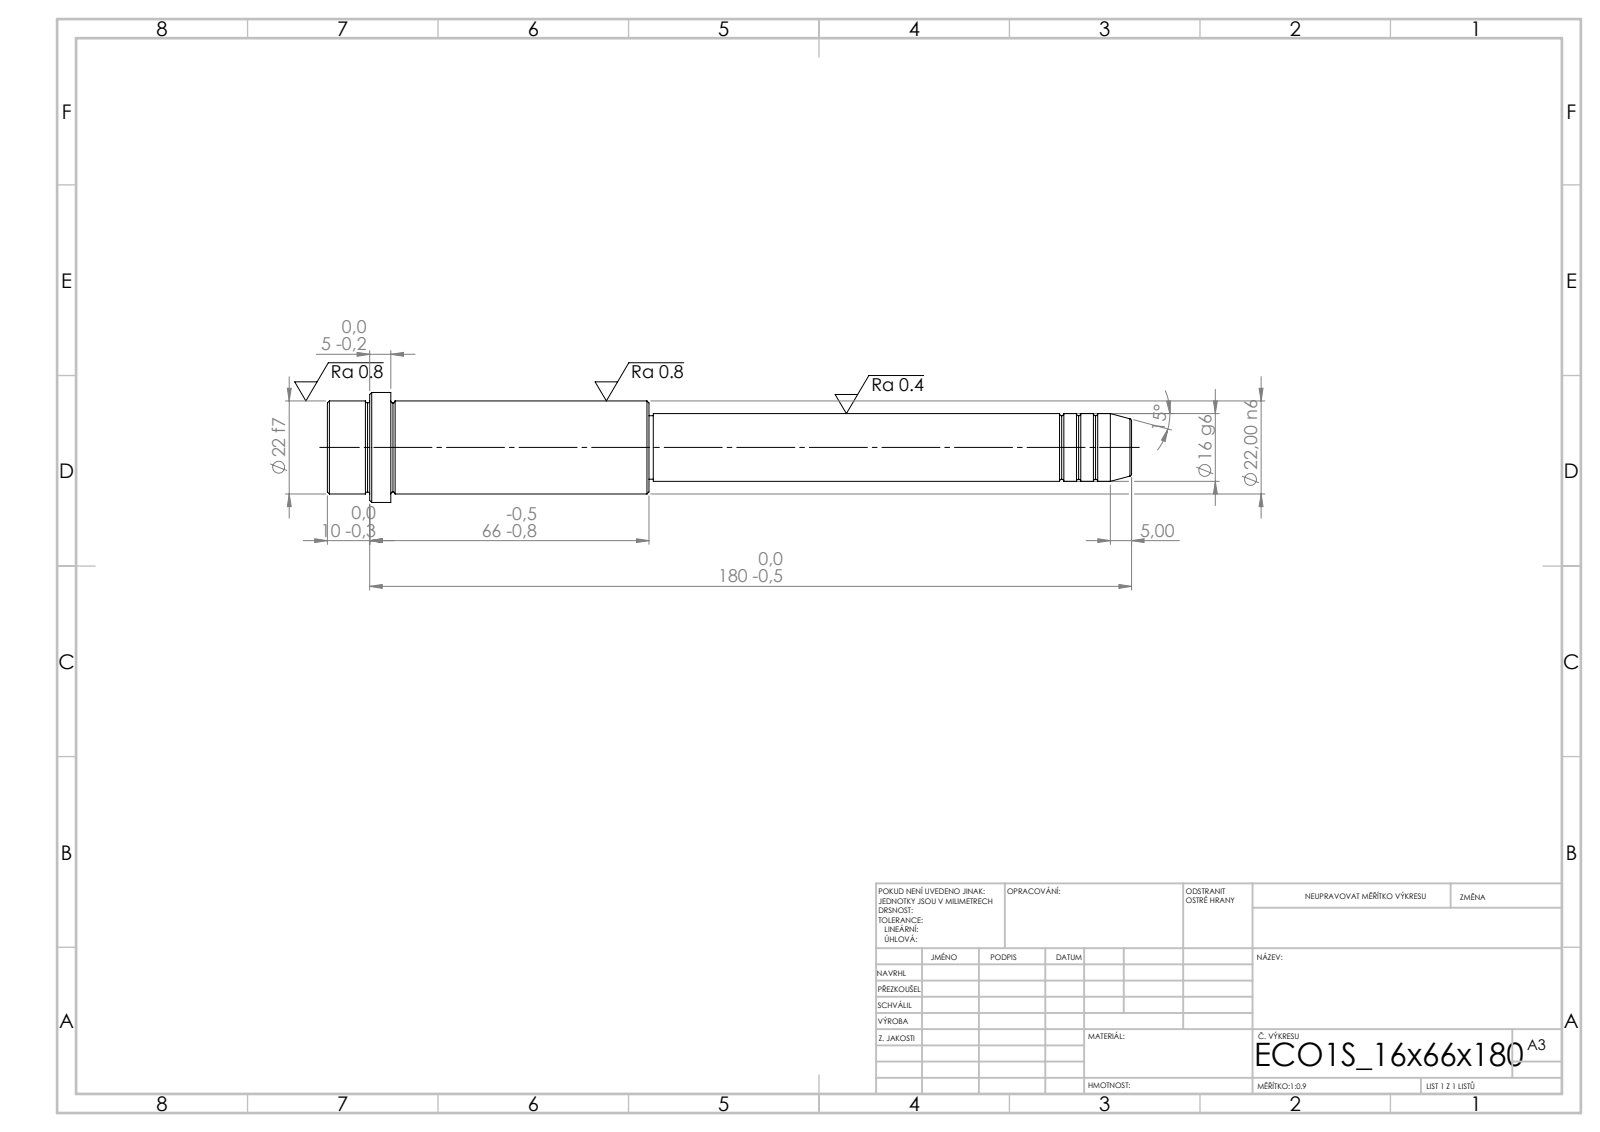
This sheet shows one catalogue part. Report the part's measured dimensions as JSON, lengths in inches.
{"step_written_by": "SolidWorks 2019 (CONFIG_CONTROL_DESIGN)", "units": "inches", "bodies": {"solids": 1, "faces": 52, "planar": 6, "cylindrical": 16, "other": 30}, "overall_size": [7.48, 1.024, 1.024], "volume_in3": 3.188, "surface_area_in2": 18.84, "round_bosses_or_shafts": [[1.024, 1], [0.866, 1], [0.63, 1], [0.591, 1]], "face_to_face_distances": [2.992, 2.402, 0.591, 4.488, 6.89, 7.48, 7.087, 2.598, 0.197, 0.394]}
